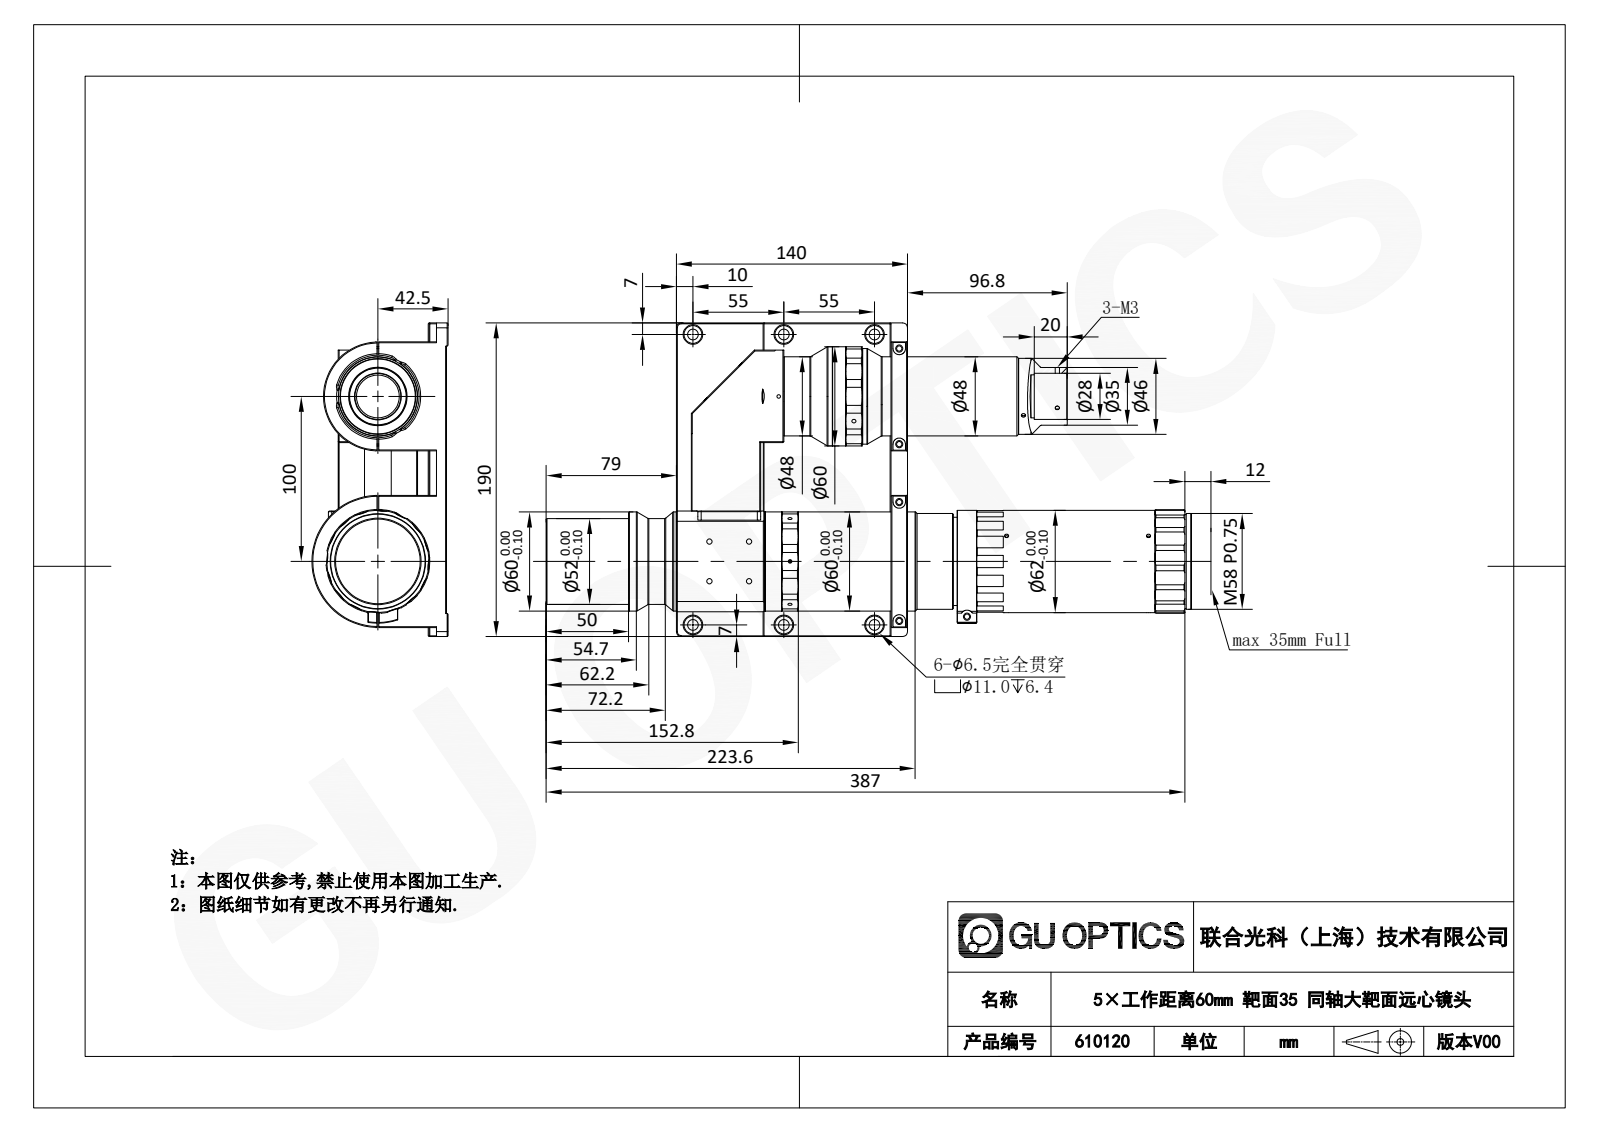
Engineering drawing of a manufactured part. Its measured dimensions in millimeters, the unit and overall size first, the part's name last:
Units: millimetres
Overall size (bounding box): 391.01 × 190 × 82.53
Round holes (diameter × count): ⌀2.5 ×25, ⌀3.3 ×24, ⌀4.5 ×13, ⌀7.5 ×8, ⌀2.4 ×7, ⌀6.5 ×6, ⌀11 ×6, ⌀6 ×4, ⌀1.5 ×2, ⌀2.2 ×2, ⌀56.1 ×2, ⌀3.4 ×1
Round bosses / shafts (diameter × count): ⌀60 ×2, ⌀58 ×2, ⌀56 ×2, ⌀62 ×1, ⌀56.8 ×1, ⌀55.9 ×1, ⌀55 ×1, ⌀54 ×1
Partial cylindrical surfaces — rounded edges, fillets, slot ends (radius × count): R15 ×32, R2 ×20, R3 ×18, R1.5 ×9, R5 ×6, R4 ×5, R0.5 ×4, R1 ×4
Main face-to-face distances: 10.5, 0.5, 11, 54.5, 6.5, 11.5, 7, 65.5, 61, 1
Hole centre spacings: 24, 41.6, 8, 30, 42.36, 6, 15.4, 30.94
Volume: 1 920 000 mm³ · Surface area: 236 471 mm²
Bodies: 1 solid, 1462 faces (440 planar, 539 cylindrical, 483 other)
Part name (STEP PRODUCT): DTCA35F-8.8C-G-M58-AL
STEP written by: SolidWorks 2017 (CONFIG_CONTROL_DESIGN)
